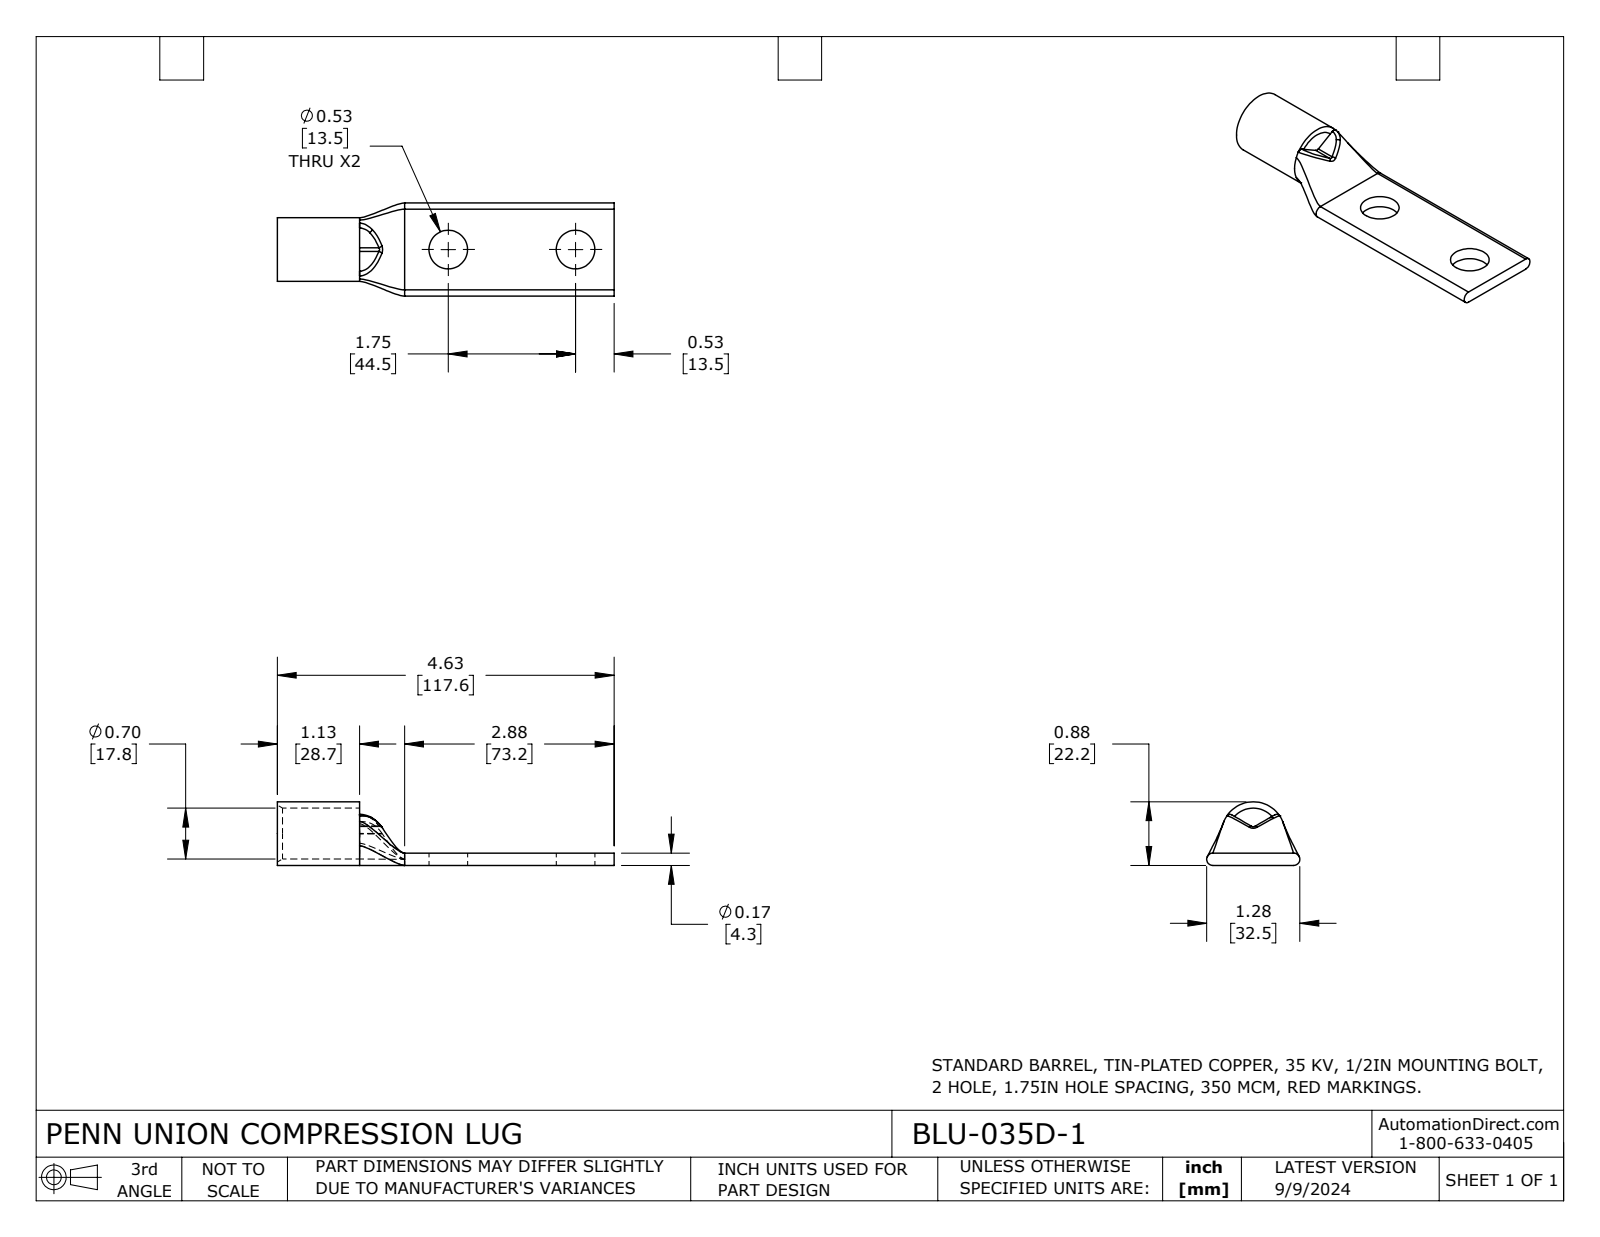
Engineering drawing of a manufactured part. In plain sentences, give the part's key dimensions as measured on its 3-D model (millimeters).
The part is named "BLU-035D-1". Its 3-D file was written by "SolidWorks 2023 (CONFIG_CONTROL_DESIGN)". It is 1 solid with 40 faces: 11 planar, 13 cylindrical and 16 other. Overall it measures 117.6 by 32.5 by 22.2 millimeters. Its volume is 14 700 cubic millimeters and its surface area 11 040 square millimeters. Round holes: 2 of diameter 13.5, 1 of diameter 17.8. Round bosses or shafts: 1 of diameter 22.2. Partial cylindrical surfaces (rounded edges, fillets, slot ends): 2 of radius 1.3, 2 of radius 2.2. The main face-to-face distances are 4.3, 117.6, 28.7, 88.9, 2.2, 44.5, 15.7, 73.2. The hole center spacings are 44.5.
